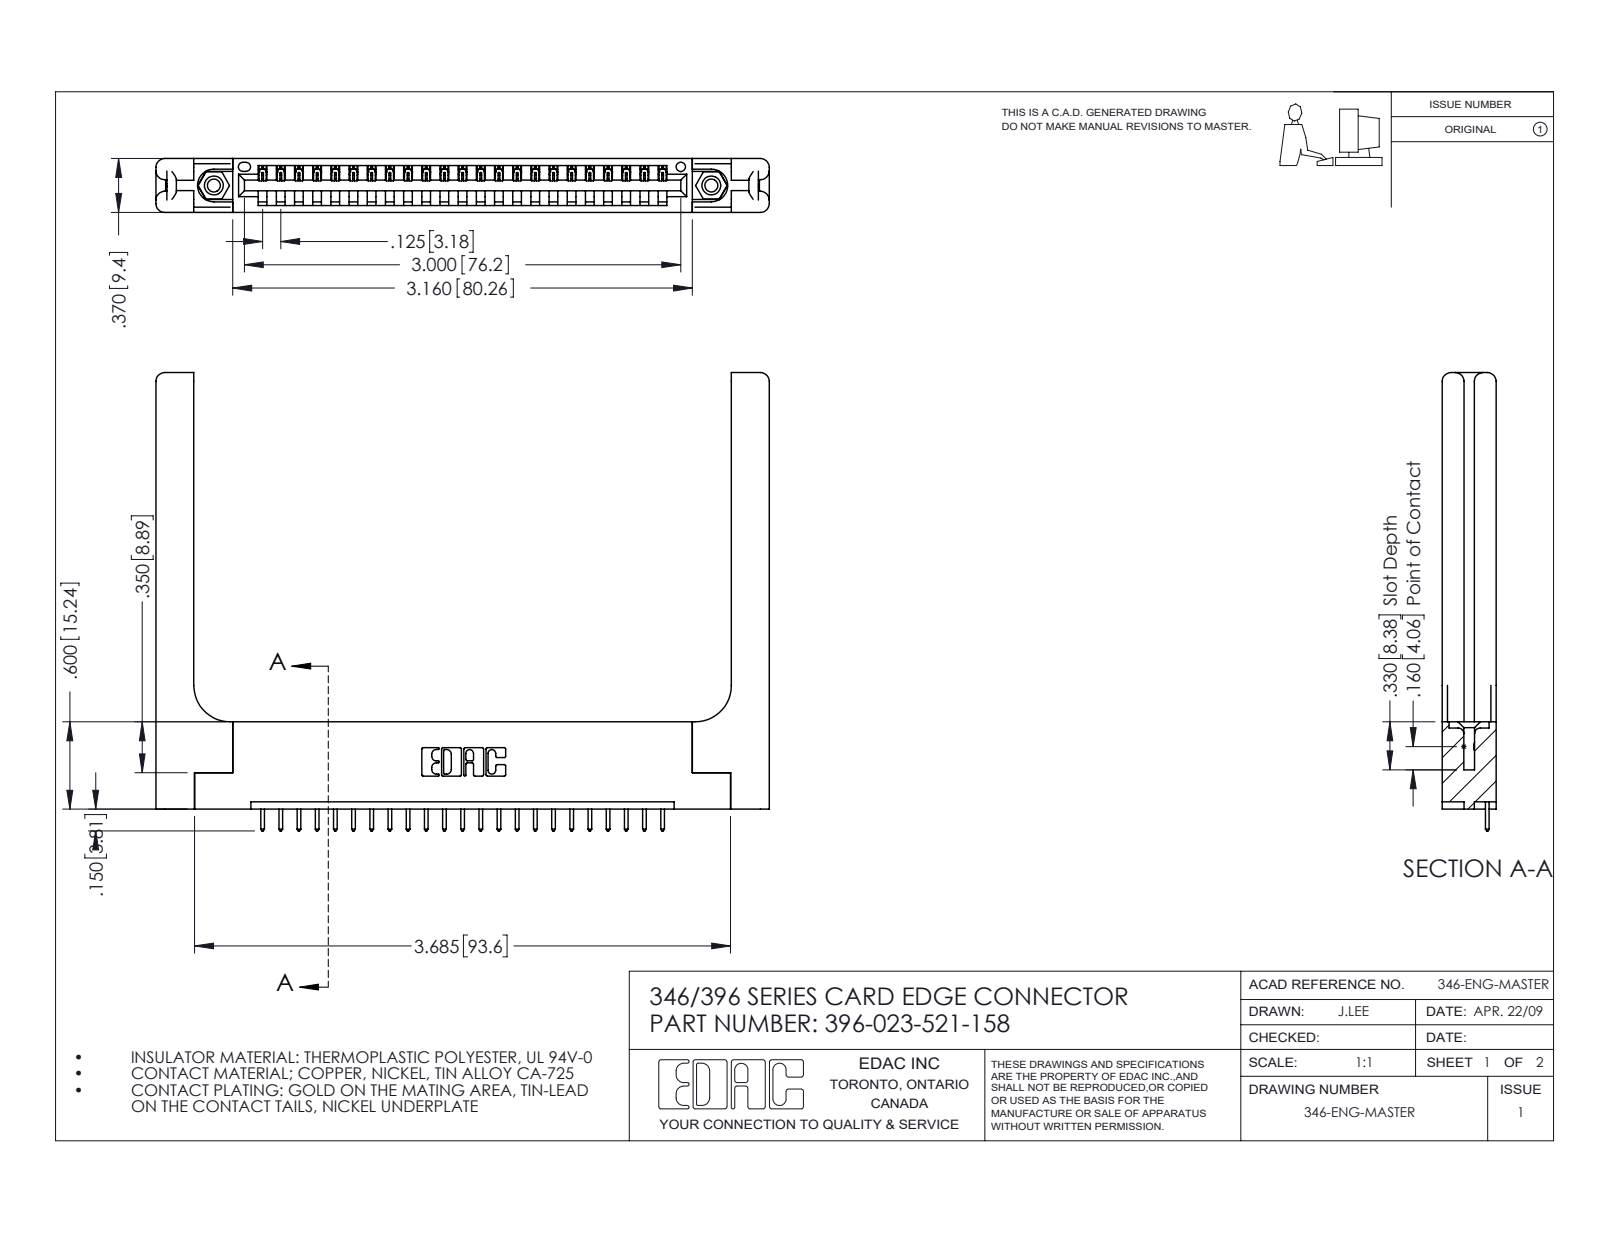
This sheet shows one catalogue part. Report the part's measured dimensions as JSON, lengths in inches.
{"part_name": "345-292-001_345-293-121; 346-220-058_345-220-058; 345-250-001_345-250-001-102; 396-023-521-158 (+1 more)", "step_written_by": "SolidWorks 2016 (CONFIG_CONTROL_DESIGN)", "units": "inches", "bodies": {"solids": 28, "faces": 1712, "planar": 1144, "cylindrical": 508, "other": 60}, "overall_size": [4.216, 3.15, 0.37], "volume_in3": 1.072, "surface_area_in2": 26.77, "round_holes": [[0.089, 2], [0.125, 2], [0.156, 2], [0.064, 1]], "round_bosses_or_shafts": [[0.155, 2]], "partial_cylinders_radius": [[0.006, 46], [0.01, 46], [0.01, 22], [0.06, 16], [0.007, 6], [0.031, 6], [0.026, 3], [0.03, 2]], "face_to_face_distances": [0.37, 0.072, 0.15, 0.148, 0.048, 0.322, 0.25, 0.298, 0.025, 0.102], "hole_center_spacings": [0.246, 3.212, 3.42]}
